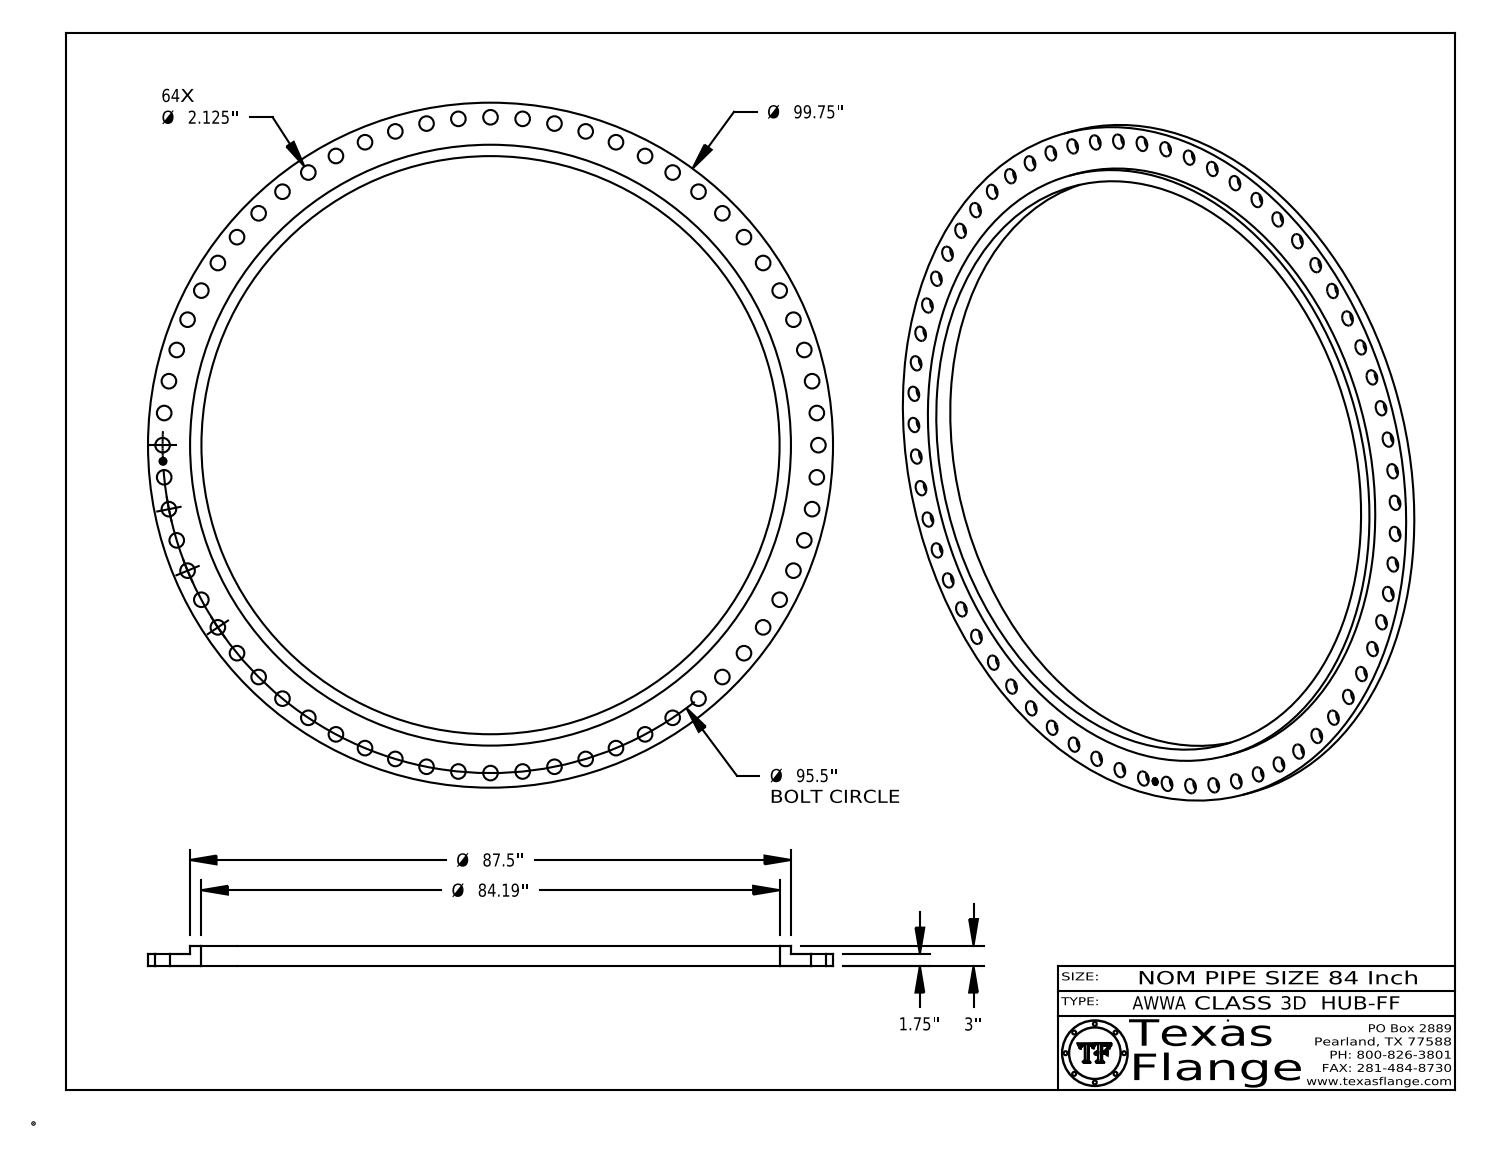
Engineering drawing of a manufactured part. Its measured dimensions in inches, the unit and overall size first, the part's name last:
Units: inches
Overall size (bounding box): 99.75 × 99.75 × 3
Round holes (diameter × count): ⌀2.125 ×64, ⌀1 ×1, ⌀84.19 ×1
Round bosses / shafts (diameter × count): ⌀0.061 ×8, ⌀99.75 ×1, ⌀87.5 ×1, ⌀0.788 ×1
Main face-to-face distances: 1.75, 3, 1.25, 0.015, 1.735, 1.265, 0.298, 0.293, 0.055, 0.193
Hole centre spacings: 9.361, 47.75, 4.686, 18.631, 23.205, 45.019, 36.546, 40.831
Volume: 4 095 in³ · Surface area: 6 475 in²
Bodies: 1 solid, 522 faces (368 planar, 154 cylindrical, 0 other)
Part name (STEP PRODUCT): AWWA Class 3D-HUB-FF
STEP written by: CATIA V5 STEP AP214 (AUTOMOTIVE_DESIGN)
